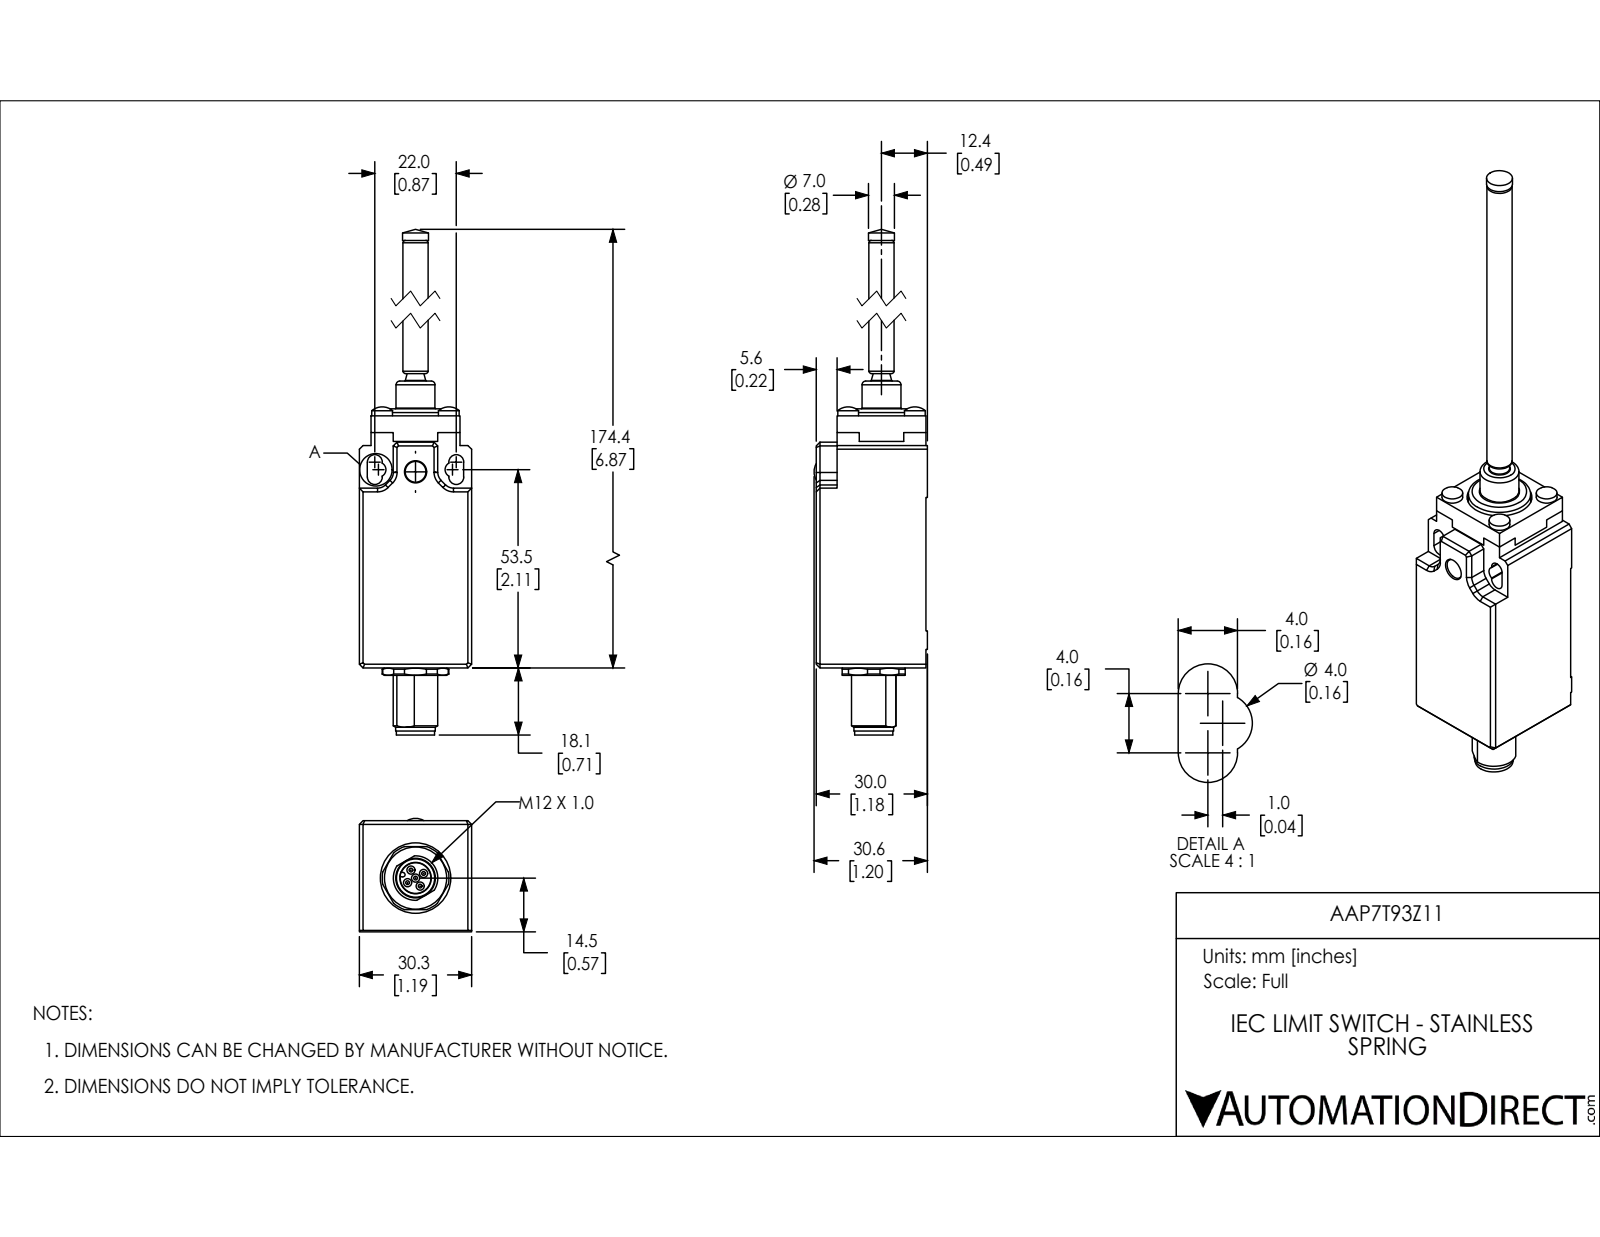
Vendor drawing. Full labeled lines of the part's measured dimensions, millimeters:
Part name (STEP PRODUCT): AAP7T93Z11
STEP written by: SolidWorks 2018 (AUTOMOTIVE_DESIGN)
Units: millimetres
Bodies: 4 solids, 281 faces (123 planar, 97 cylindrical, 61 other)
Overall size (bounding box): 192.5 × 30.6 × 30.3
Volume: 62 880 mm³ · Surface area: 17 400 mm²
Round holes (diameter × count): ⌀2.2 ×5, ⌀6 ×1, ⌀13 ×1, ⌀14 ×1, ⌀16 ×1, ⌀17.5 ×1
Round bosses / shafts (diameter × count): ⌀5.6 ×5, ⌀1.4 ×5, ⌀1 ×5, ⌀16.8 ×1, ⌀10.7 ×1, ⌀10.5 ×1, ⌀10.3 ×1, ⌀7 ×1
Partial cylindrical surfaces — rounded edges, fillets, slot ends (radius × count): R2 ×6, R3 ×4, R0.6 ×1, R6 ×1, R9 ×1, R10 ×1, R10.2 ×1
Main face-to-face distances: 30.3, 29.6, 61.1, 0.4, 30, 24, 3.1, 27.2, 6, 5.6
Hole centre spacings: 2.5, 3.5, 5, 0.6, 2.1, 2.9, 3.6, 4.6
